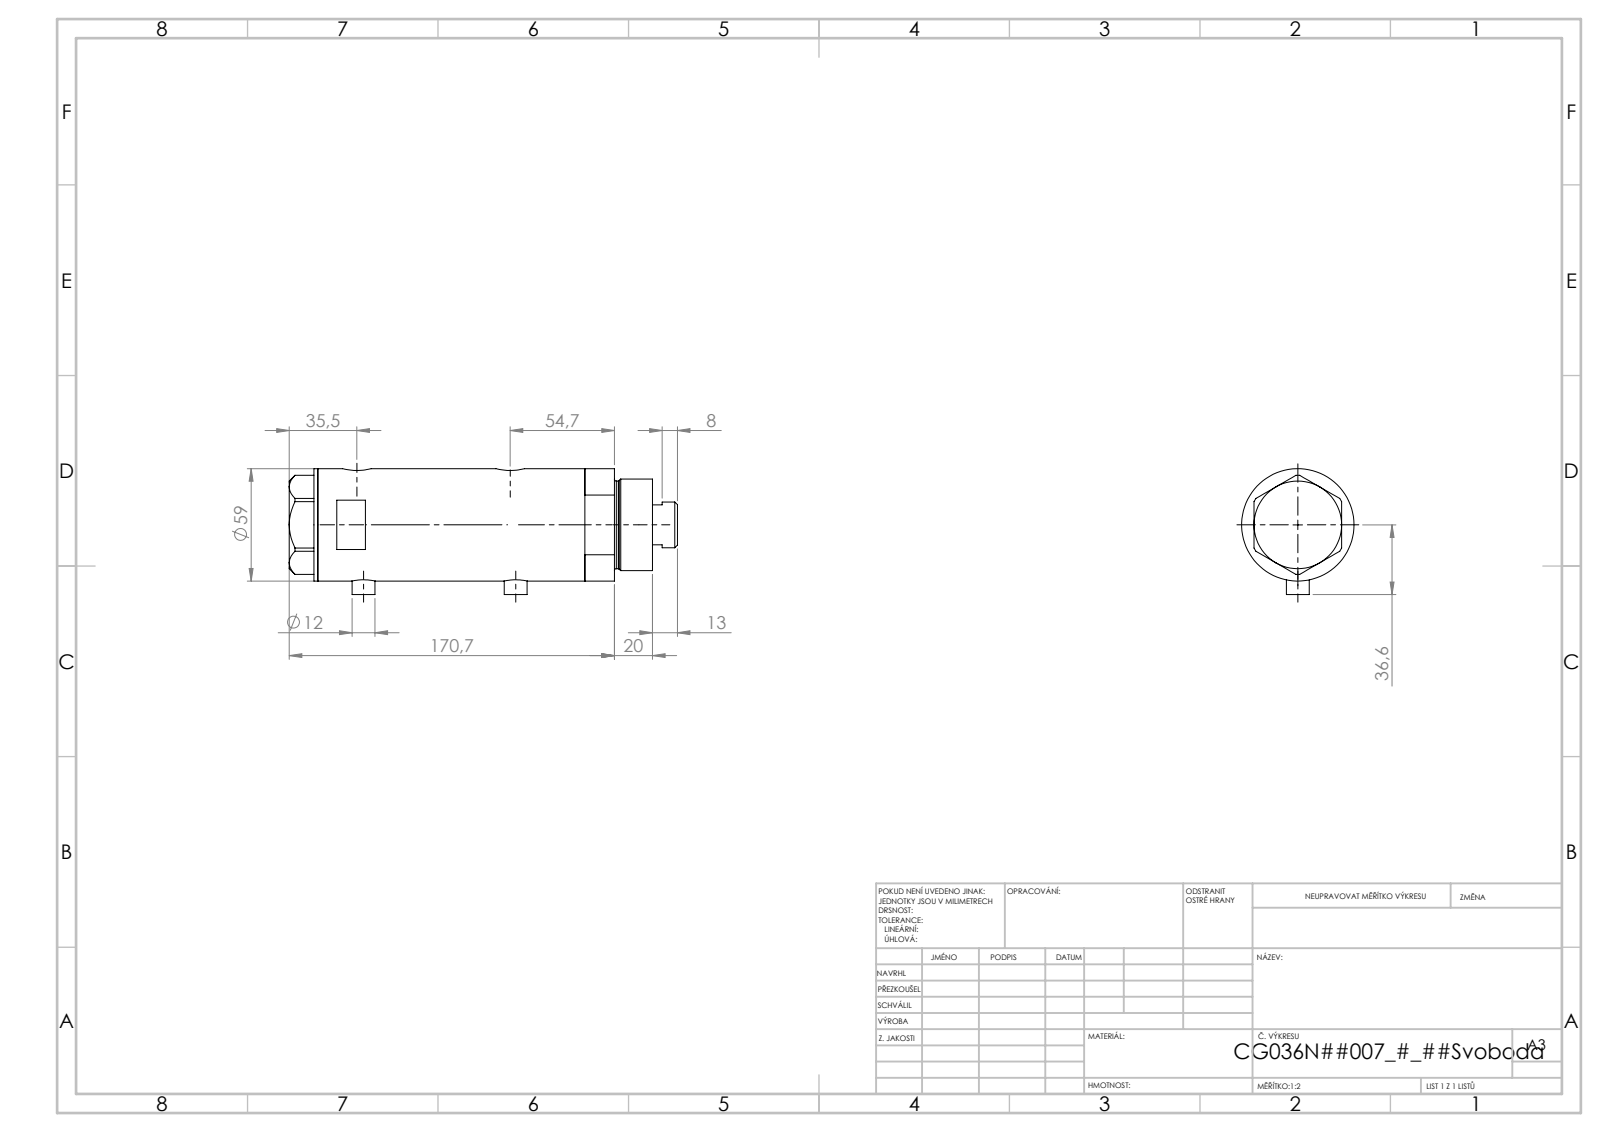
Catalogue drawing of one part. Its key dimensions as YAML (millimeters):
part_name: "V270CG_FRONT; V270CG_BACK; V270CG_MIDDLE; V270CG_VC"
step_written_by: "SolidWorks 2019 (CONFIG_CONTROL_DESIGN)"
units: millimeters
bodies: {solids: 4, faces: 126, planar: 53, cylindrical: 53, other: 20}
overall_size: [203.8, 66.1, 59]
volume: 484608
surface_area: 99744
round_holes:
  - {diameter: 5, count: 2}
  - {diameter: 9.73, count: 2}
  - {diameter: 12.5, count: 2}
  - {diameter: 15, count: 2}
  - {diameter: 8.5, count: 1}
  - {diameter: 25, count: 1}
  - {diameter: 26.5, count: 1}
  - {diameter: 36, count: 1}
  - {diameter: 40, count: 1}
  - {diameter: 52, count: 1}
round_bosses_or_shafts:
  - {diameter: 12, count: 2}
  - {diameter: 59, count: 1}
  - {diameter: 48, count: 1}
  - {diameter: 46, count: 1}
  - {diameter: 24, count: 1}
face_to_face_distances: [102.2, 23.5, 78.7, 15, 38.5, 117.2, 2, 175.7, 190.7, 152.2]
hole_center_spacings: [2.9, 3.5, 77, 79.9, 80.5, 83.4]
